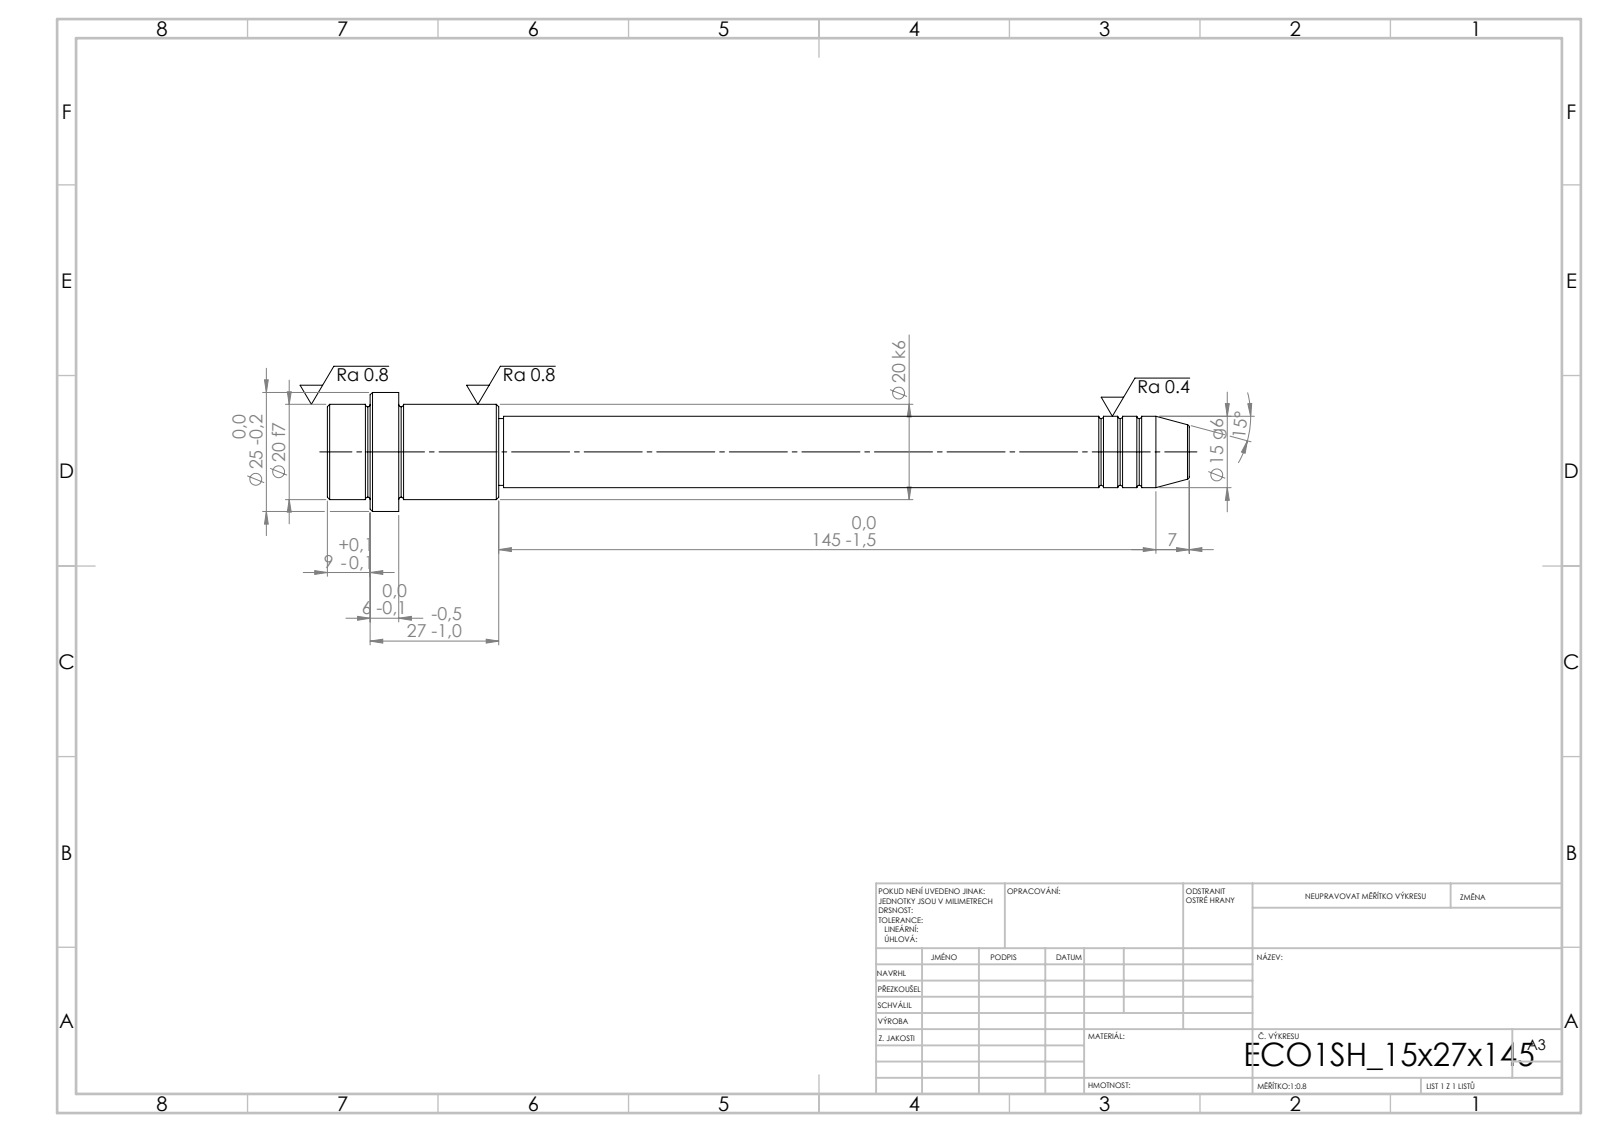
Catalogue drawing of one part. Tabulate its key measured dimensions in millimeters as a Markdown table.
| quantity | value |
| --- | --- |
| STEP written by | SolidWorks 2019 (CONFIG_CONTROL_DESIGN) |
| units | millimeters |
| bodies | 1 solid, 52 faces (6 planar, 16 cylindrical, 30 other) |
| overall size | 181 × 25 × 25 |
| volume | 37 559 mm³ |
| surface area | 10 177 mm² |
| round bosses / shafts (diameter × count) | 25 × 1, 20 × 1, 15 × 1, 14 × 1 |
| main face-to-face distances | 15, 6, 9, 21, 27, 36, 145, 166, 172, 181 |
